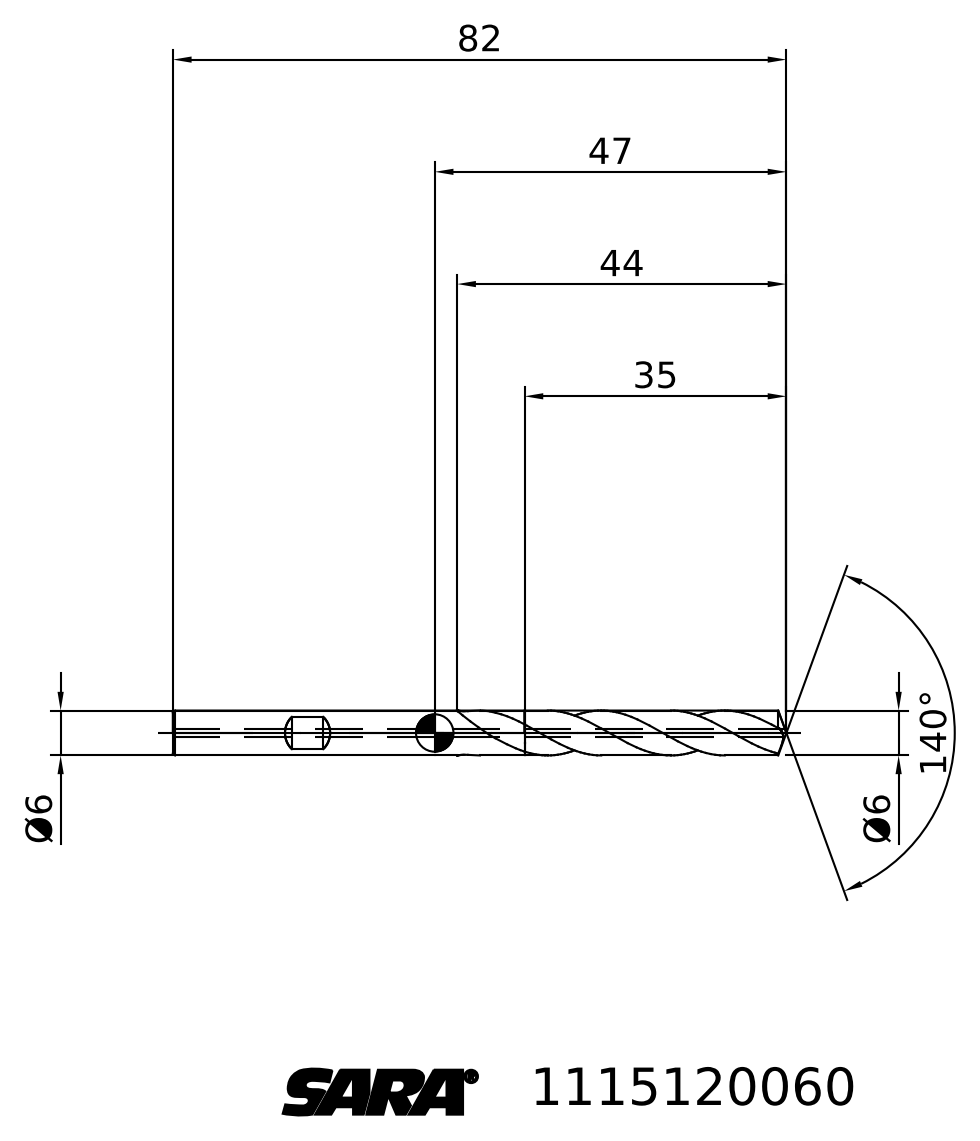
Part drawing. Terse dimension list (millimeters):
written by: TDM (AUTOMOTIVE_DESIGN)
unit: mm
bodies: 2 solids, 29 faces (6 planar, 0 cylindrical, 23 other)
size: 82 × 8.17 × 6
volume: 1 880 mm³; area: 1 685 mm²
face distances: 47
